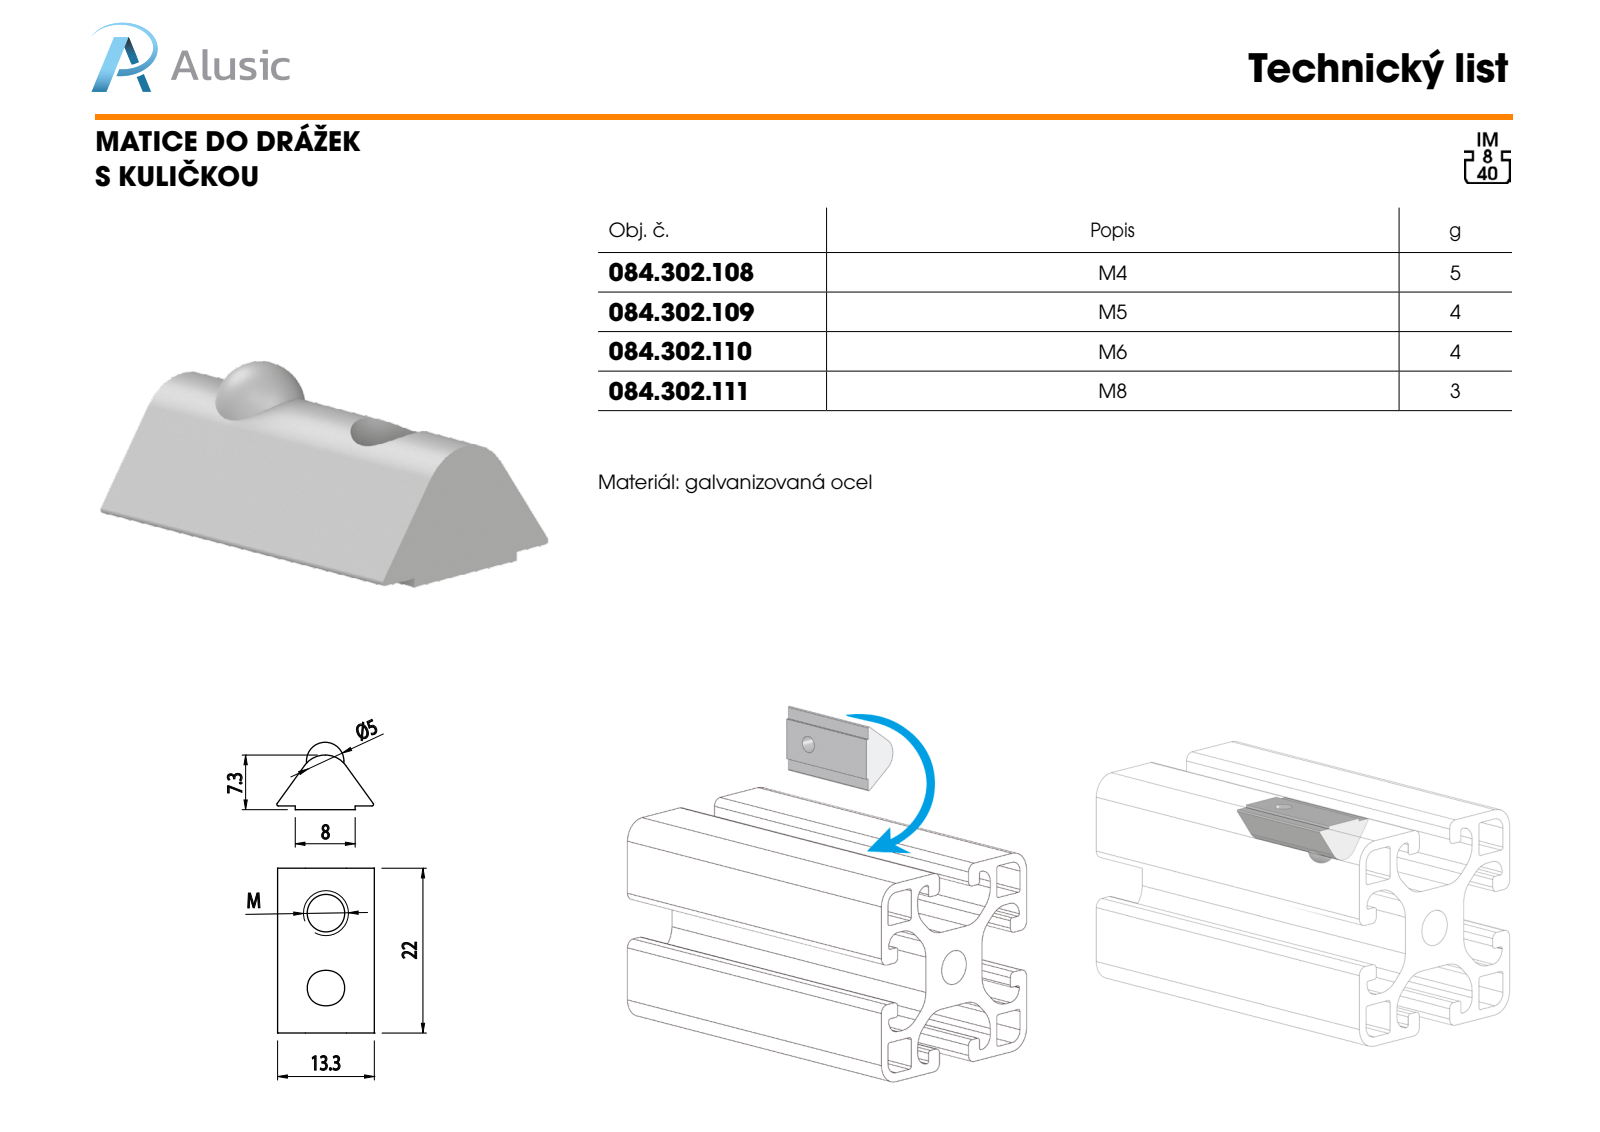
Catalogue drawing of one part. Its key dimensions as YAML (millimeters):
part_name: "084.302.111"
step_written_by: "SolidWorks 2016 (CONFIG_CONTROL_DESIGN)"
units: millimeters
bodies: {solids: 1, faces: 17, planar: 9, cylindrical: 7, other: 1}
overall_size: [22, 12.92, 9]
volume: 1097
surface_area: 921
round_holes:
  - {diameter: 6.8, count: 1}
partial_cylinders:
  - {radius: 0.2, count: 2}
  - {radius: 3.4, count: 1}
face_to_face_distances: [0.5, 22, 8]
